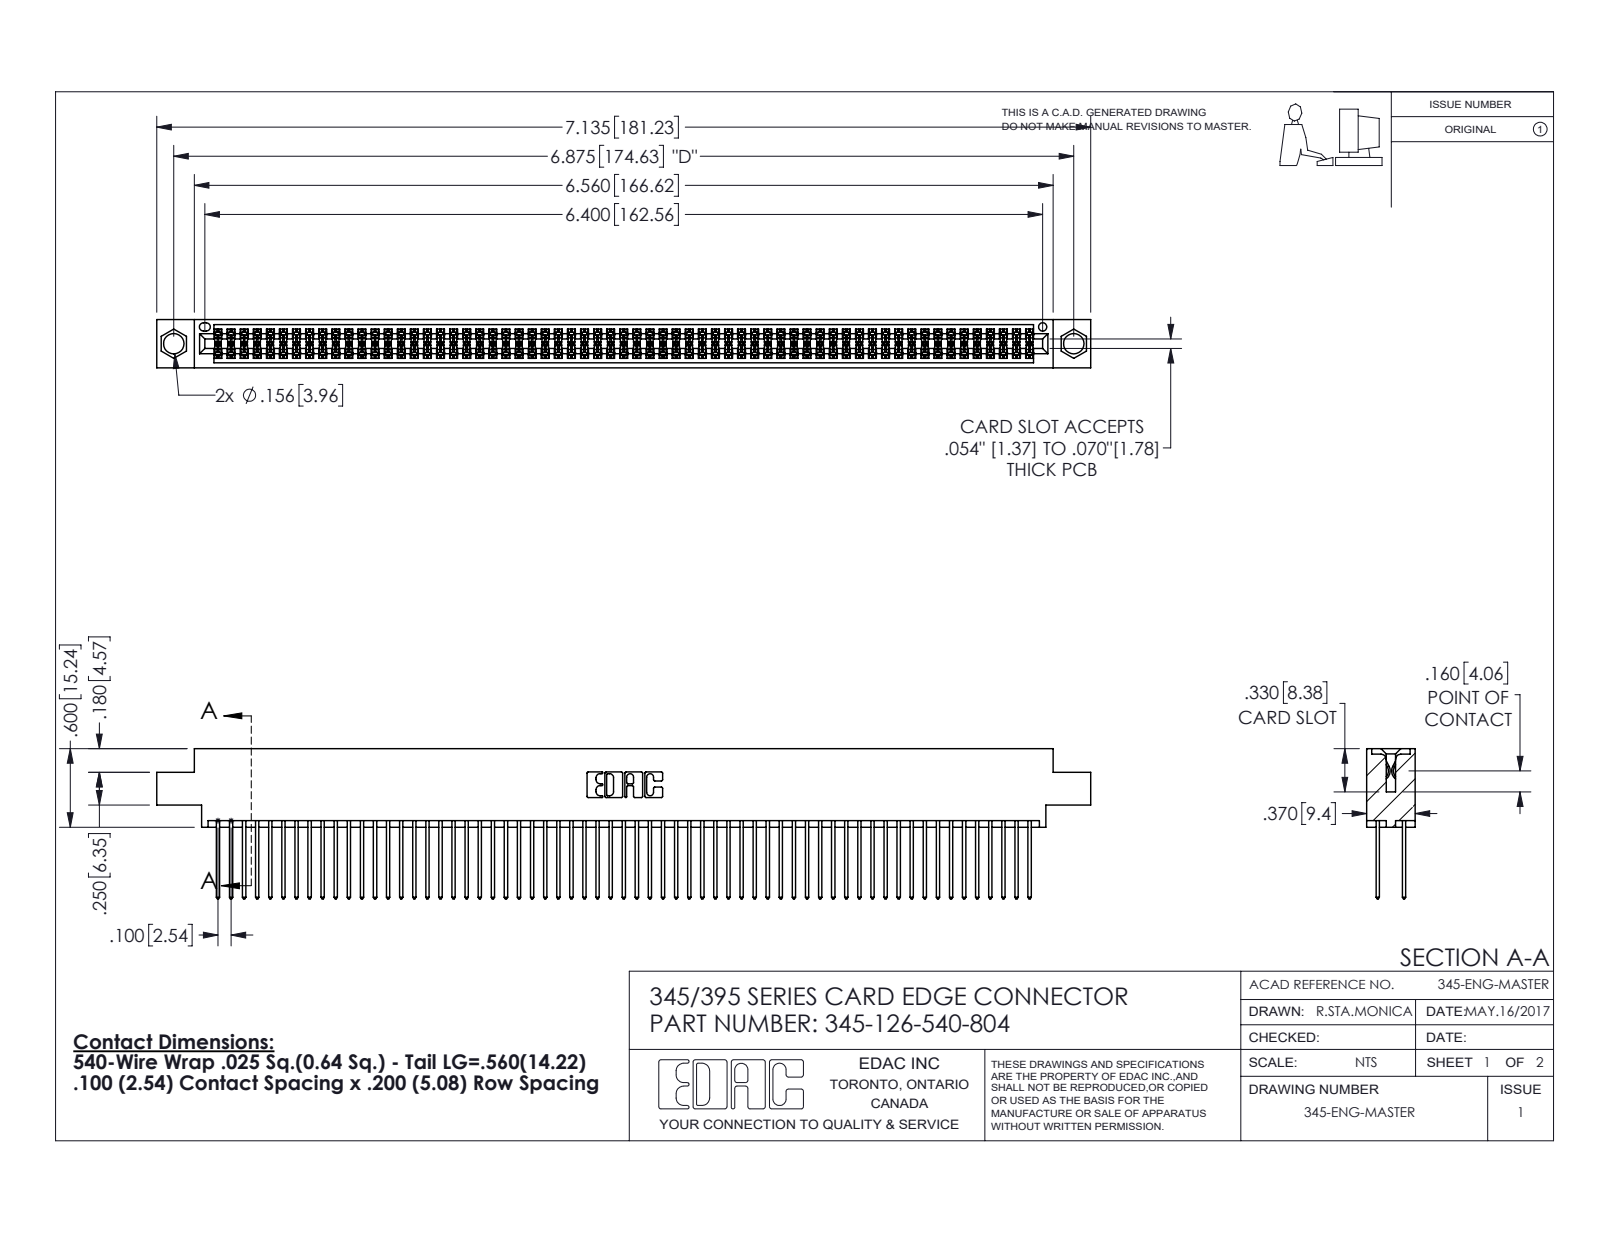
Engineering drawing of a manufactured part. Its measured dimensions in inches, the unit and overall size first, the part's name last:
Units: inches
Overall size (bounding box): 7.135 × 1.147 × 0.37
Round holes (diameter × count): ⌀0.156 ×2, ⌀0.064 ×1
Partial cylindrical surfaces — rounded edges, fillets, slot ends (radius × count): R0.006 ×189, R0.01 ×126, R0.01 ×22, R0.007 ×6, R0.031 ×6, R0.026 ×3, R0.014 ×2, R0.019 ×2
Main face-to-face distances: 0.298, 0.072, 0.2, 0.098, 0.272, 0.025, 0.37, 0.225, 0.175, 0.149
Hole centre spacings: 0.27, 6.639, 6.875
Volume: 1.102 in³ · Surface area: 45.43 in²
Bodies: 127 solids, 6444 faces (4256 planar, 2188 cylindrical, 0 other)
Part name (STEP PRODUCT): 345-126-540-804; 345 Part_0.170 Offset - 0.156 Dia-TI; 345-292-001_345-293-140
STEP written by: SolidWorks 2020 (CONFIG_CONTROL_DESIGN)
